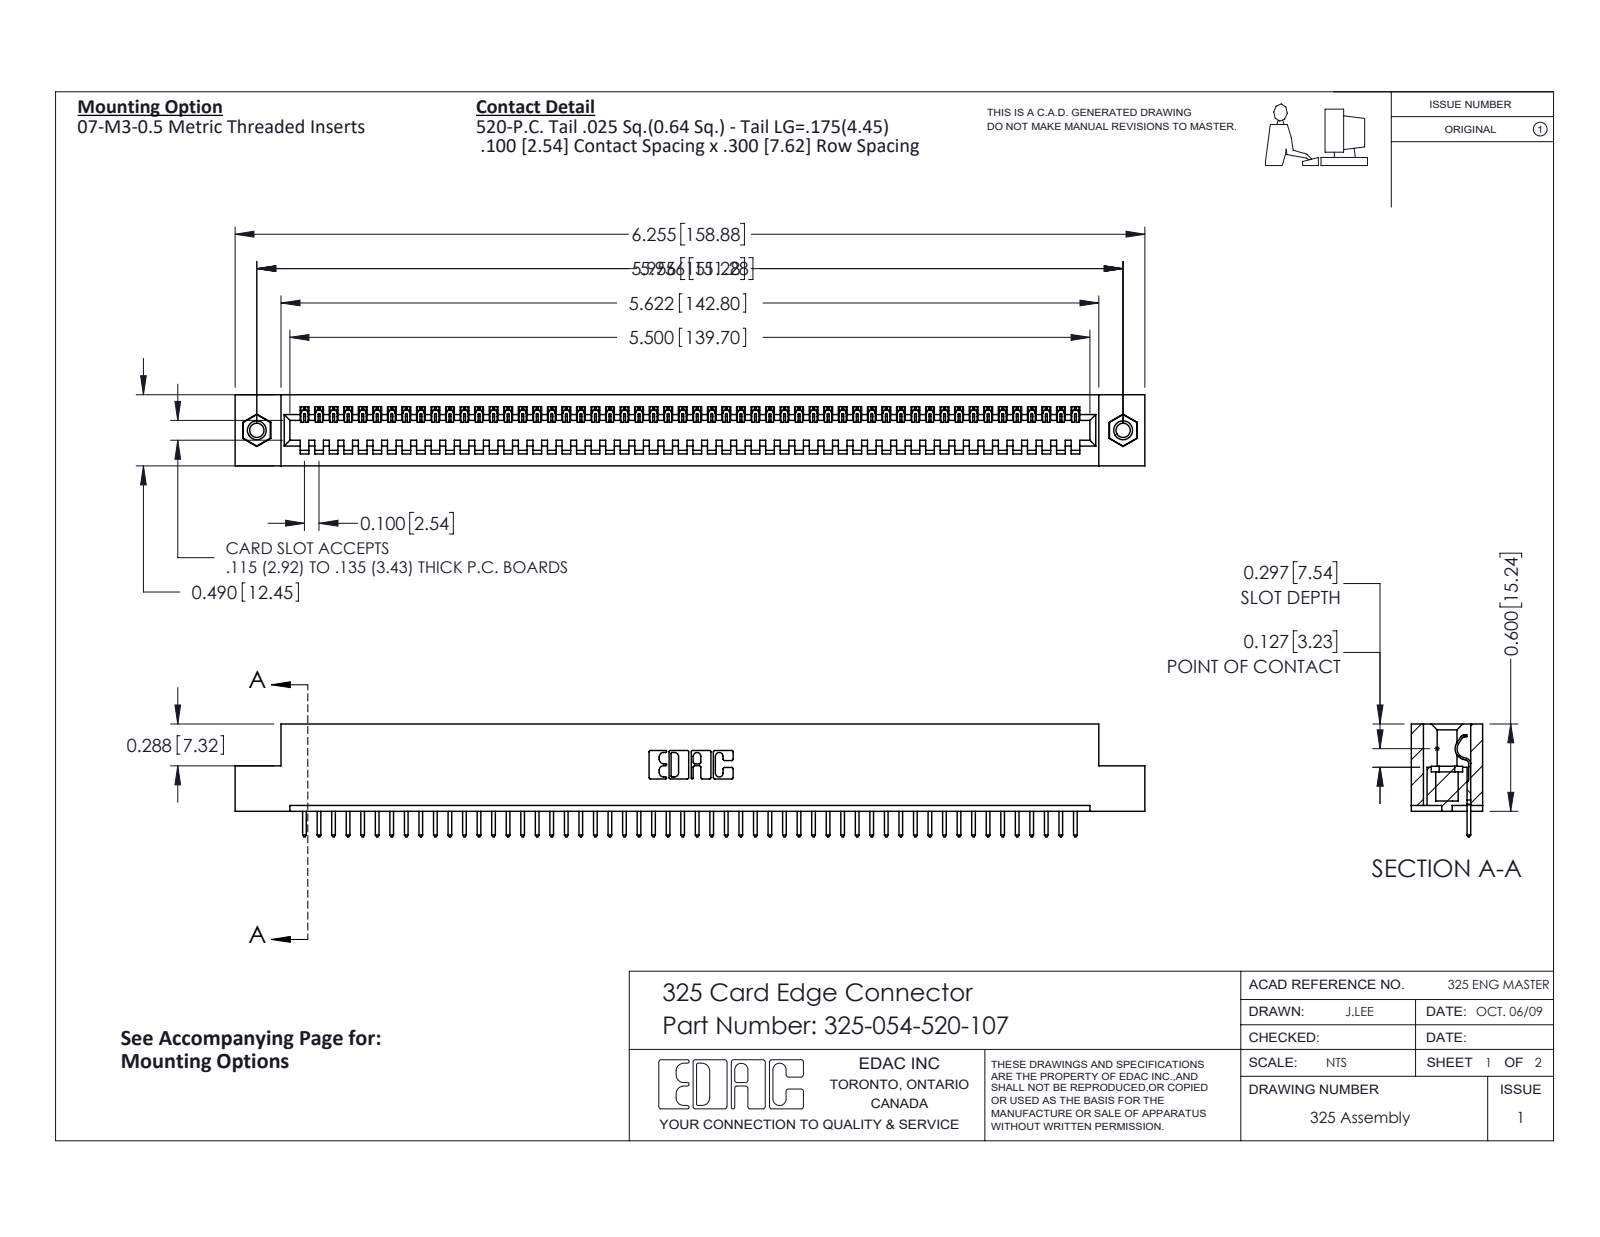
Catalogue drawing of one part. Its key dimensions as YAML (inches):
part_name: "325-054-520-107; 325 Part_TI; 325-292-001_325-293-120; 345-250-001_345-250-005-103"
step_written_by: "SolidWorks 2016 (CONFIG_CONTROL_DESIGN)"
units: inches
bodies: {solids: 57, faces: 3306, planar: 2370, cylindrical: 920, other: 16}
overall_size: [6.255, 0.775, 0.49]
volume: 1.227
surface_area: 33.53
round_holes:
  - {diameter: 0.098, count: 2}
  - {diameter: 0.125, count: 2}
  - {diameter: 0.16, count: 2}
round_bosses_or_shafts:
  - {diameter: 0.155, count: 2}
partial_cylinders:
  - {radius: 0.006, count: 108}
  - {radius: 0.01, count: 108}
  - {radius: 0.01, count: 22}
  - {radius: 0.007, count: 6}
  - {radius: 0.031, count: 6}
  - {radius: 0.026, count: 3}
  - {radius: 0.014, count: 1}
  - {radius: 0.022, count: 1}
face_to_face_distances: [0.083, 0.407, 0.49, 0.3, 0.107, 0.383, 0.025, 0.325, 0.56, 0.263]
hole_center_spacings: [5.956]
